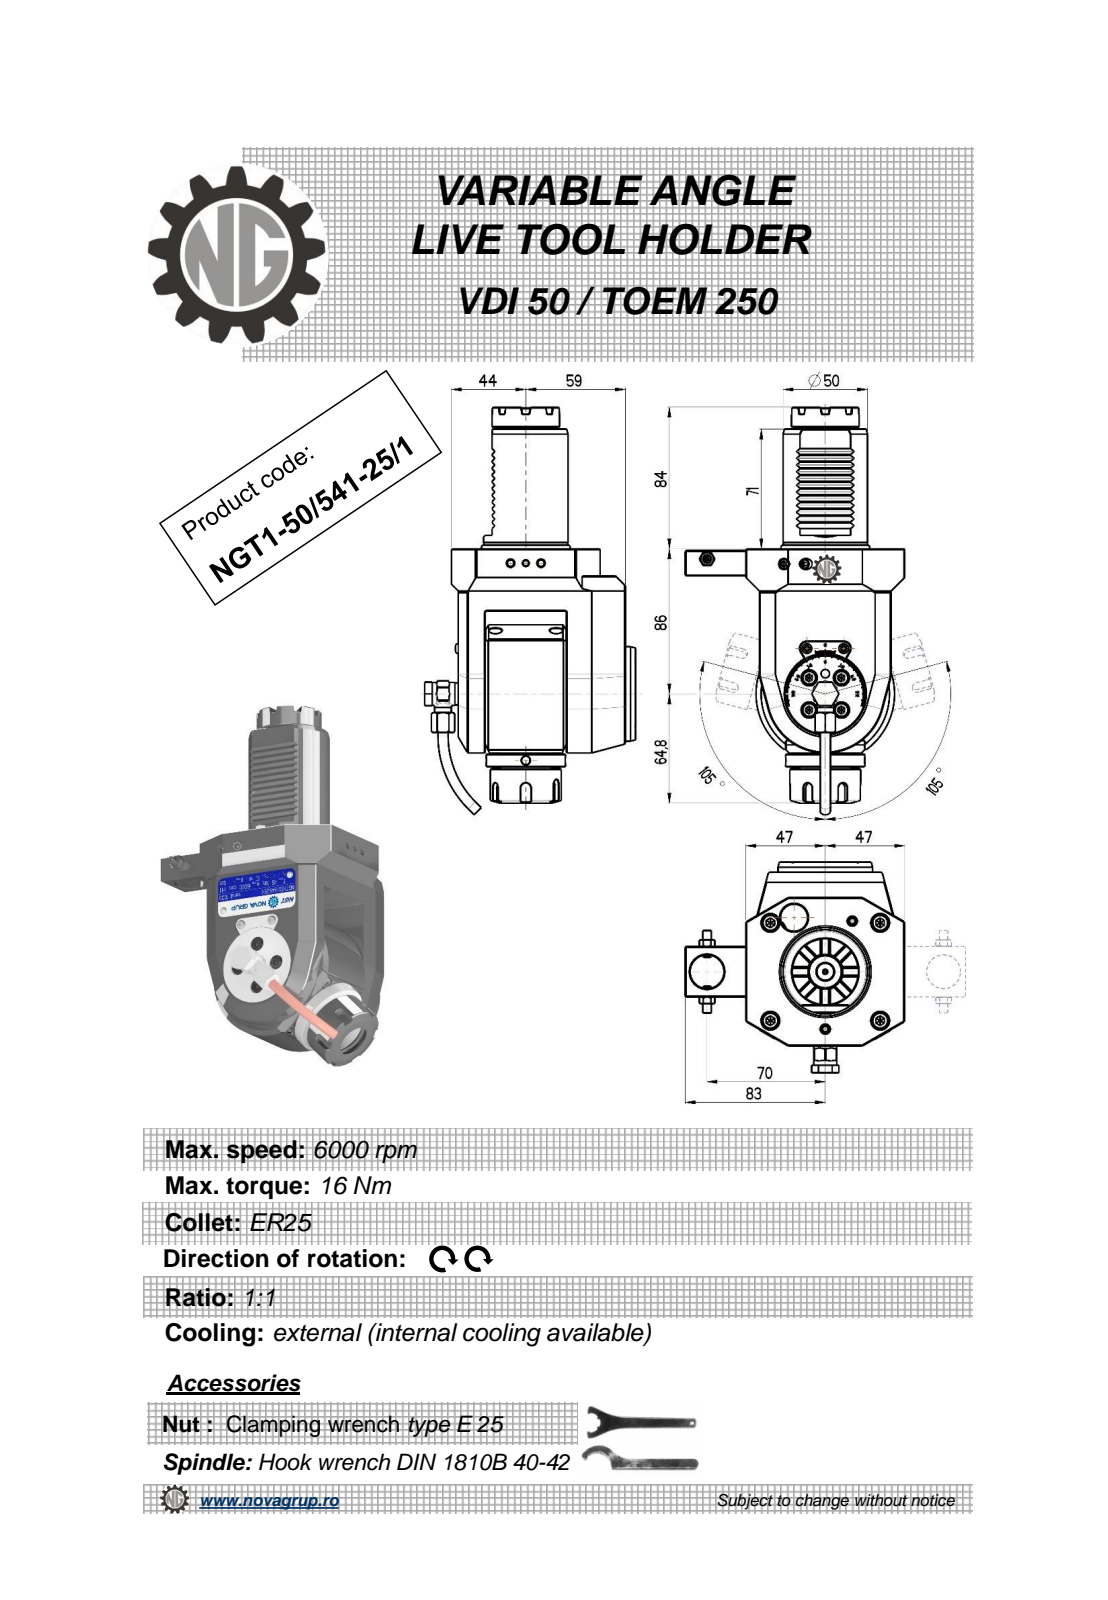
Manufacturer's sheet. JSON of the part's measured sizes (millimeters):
{"part_name": "NGT1_50_541_25_1", "step_written_by": "PRO/ENGINEER BY PARAMETRIC TECHNOLOGY CORPORATION, 2010280 (CONFIG_CONTROL_DESIGN)", "units": "millimeters", "bodies": {"solids": 1, "faces": 689, "planar": 307, "cylindrical": 144, "other": 238}, "overall_size": [241.67, 130, 124.9], "volume_mm3": 1022000, "surface_area_mm2": 94158, "round_holes": [[4, 3], [5, 2], [3, 1], [5.4, 1], [6.2, 1], [9, 1], [9.5, 1], [10, 1], [11, 1], [20, 1], [20.3, 1]], "round_bosses_or_shafts": [[6, 2], [5.7, 2], [82, 1], [56, 1], [50, 1], [47, 1], [42, 1], [40, 1]], "partial_cylinders_radius": [[0.26, 12], [0.3, 12], [0.16, 6], [3, 5], [0.5, 4], [1, 2], [10, 2], [7.7, 1]], "face_to_face_distances": [37, 16, 99, 8, 64, 6, 21, 105, 20, 35], "hole_center_spacings": [0.4, 39.45, 49, 49.4, 70, 85.45, 85.68, 116.95]}
